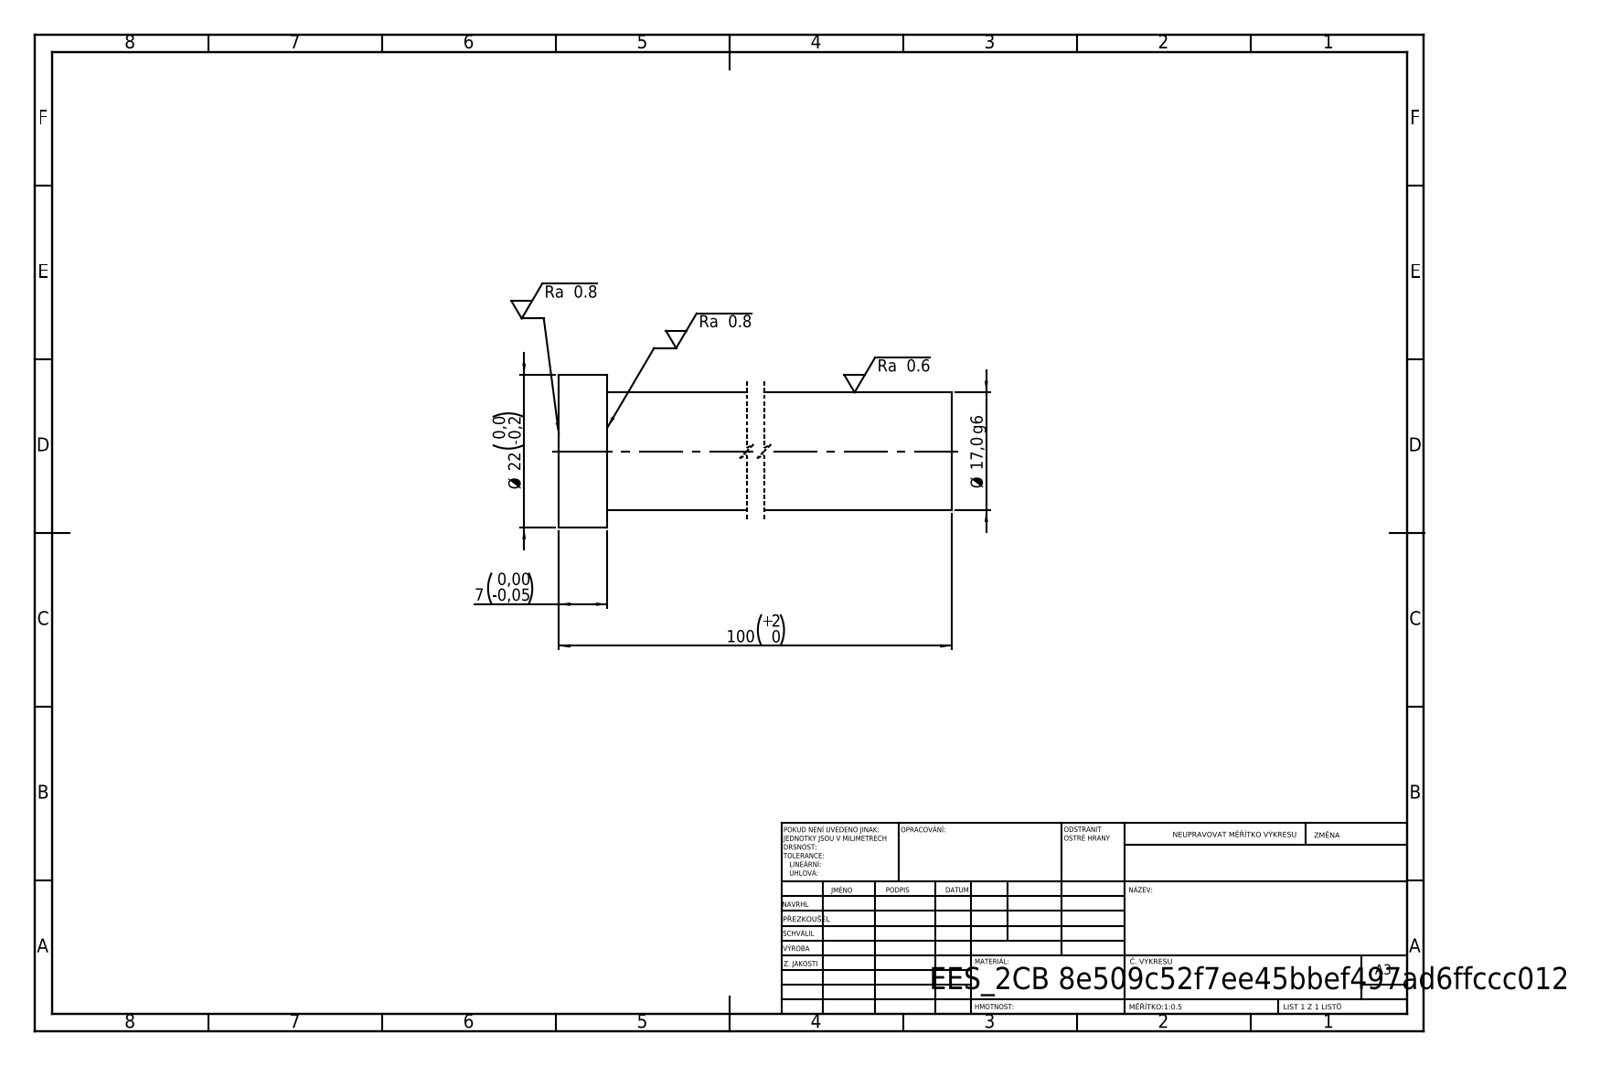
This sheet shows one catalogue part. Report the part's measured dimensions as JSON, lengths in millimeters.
{"step_written_by": "SolidWorks 2019 (CONFIG_CONTROL_DESIGN)", "units": "millimeters", "bodies": {"solids": 1, "faces": 7, "planar": 3, "cylindrical": 4, "other": 0}, "overall_size": [100, 22, 22], "volume_mm3": 23770, "surface_area_mm2": 6211, "round_bosses_or_shafts": [[22, 1], [17, 1]], "face_to_face_distances": [100, 7, 93]}
